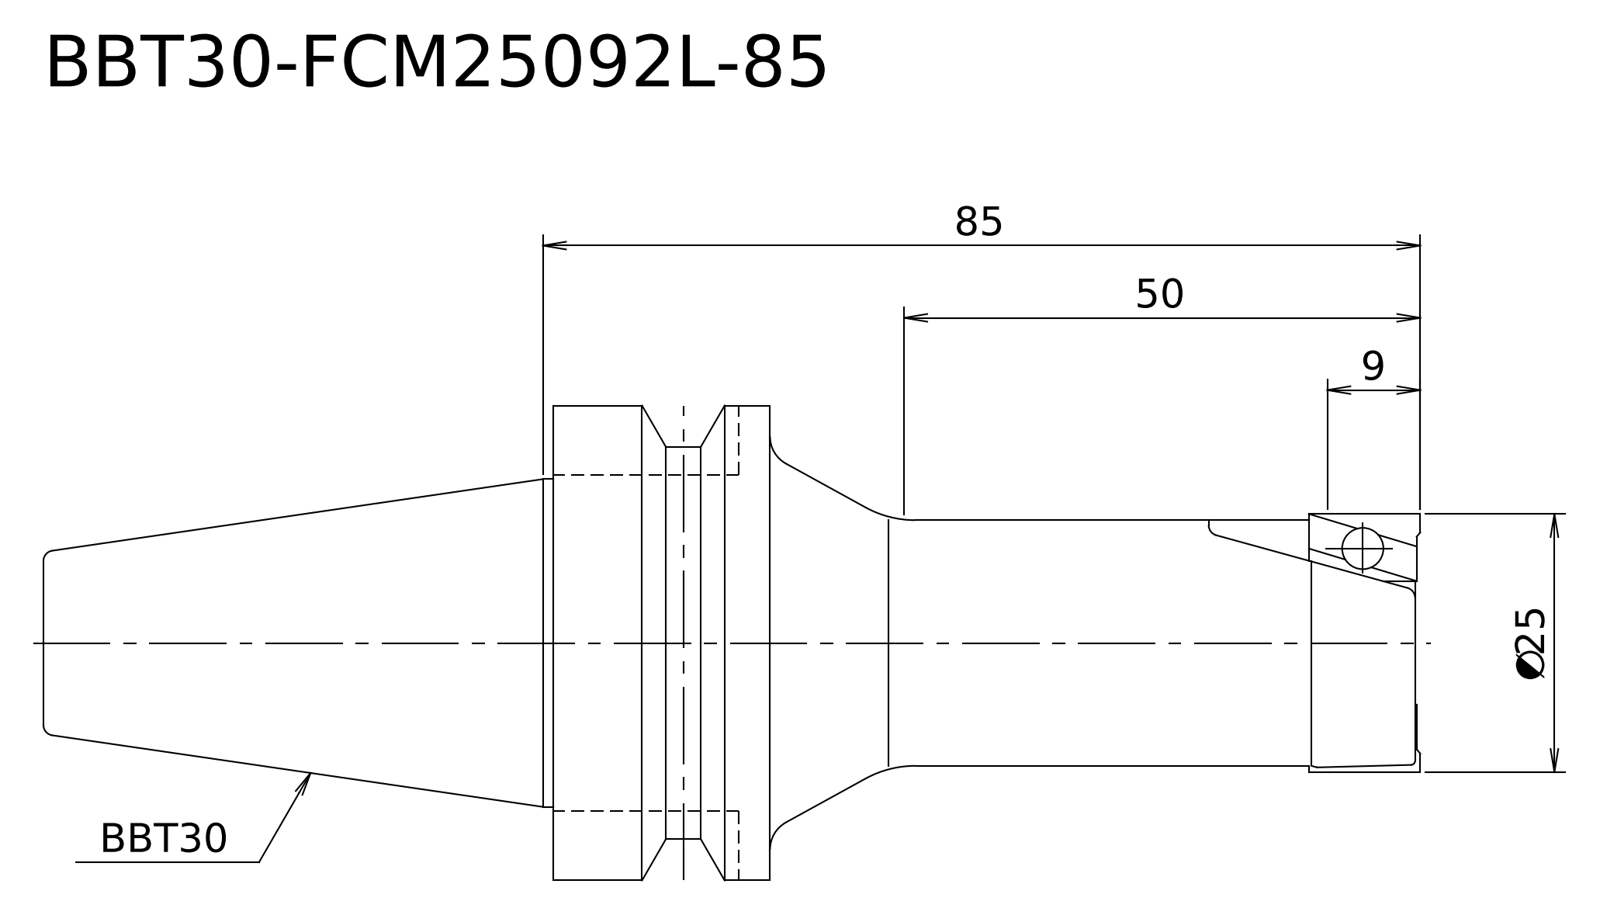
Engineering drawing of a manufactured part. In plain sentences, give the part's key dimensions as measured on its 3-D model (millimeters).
Its 3-D file was written by "Kubotek KeyCreator V8.5.1 (14335) (CONFIG_CONTROL_DESIGN)". It is 1 solid with 17 faces: 4 planar, 6 cylindrical and 7 other. Overall it measures 133.4 by 46 by 46 millimeters. Its volume is 88 419 cubic millimeters and its surface area 14 701 square millimeters. Round bosses or shafts: 1 of diameter 46, 1 of diameter 38, 1 of diameter 31.75, 1 of diameter 25, 1 of diameter 23.8. The main face-to-face distances are 84, 63, 21, 133.4, 70.4, 49.4.
